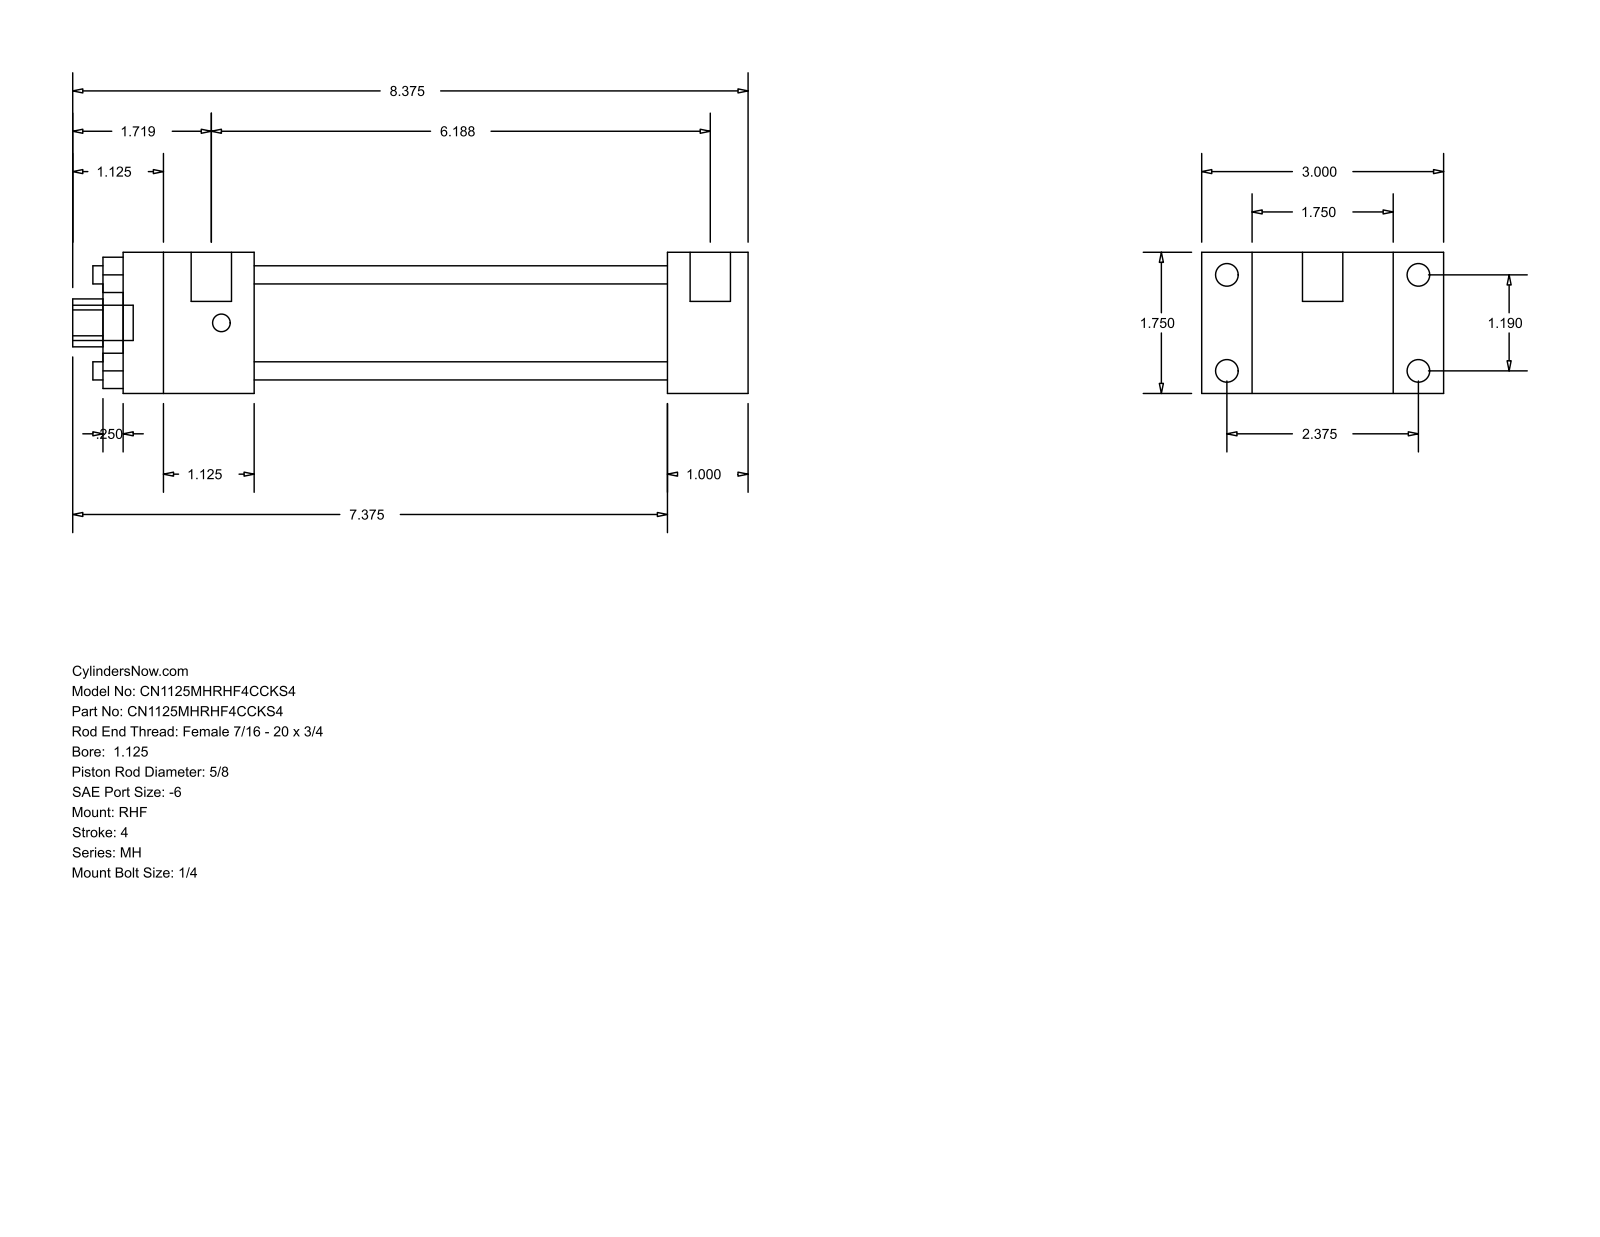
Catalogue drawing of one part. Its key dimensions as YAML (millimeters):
part_name: "MH_RHF__0112_0.625"
step_written_by: "GSSL Pune (CONFIG_CONTROL_DESIGN)"
units: millimeters
bodies: {solids: 0, faces: 88, planar: 60, cylindrical: 28, other: 0}
overall_size: [212.72, 76.2, 44.45]
round_holes:
  - {diameter: 5.71, count: 4}
  - {diameter: 15.88, count: 1}
  - {diameter: 28.57, count: 1}
  - {diameter: 34.92, count: 1}
round_bosses_or_shafts:
  - {diameter: 7.14, count: 4}
  - {diameter: 5.56, count: 4}
  - {diameter: 12.7, count: 2}
  - {diameter: 11.11, count: 1}
partial_cylinders:
  - {radius: 7.54, count: 1}
face_to_face_distances: [44.46, 15.87, 60.33, 25.4, 76.2, 130.17, 155.57, 41.27, 171.44, 196.84]
hole_center_spacings: [21.37, 30.22, 42.74]
